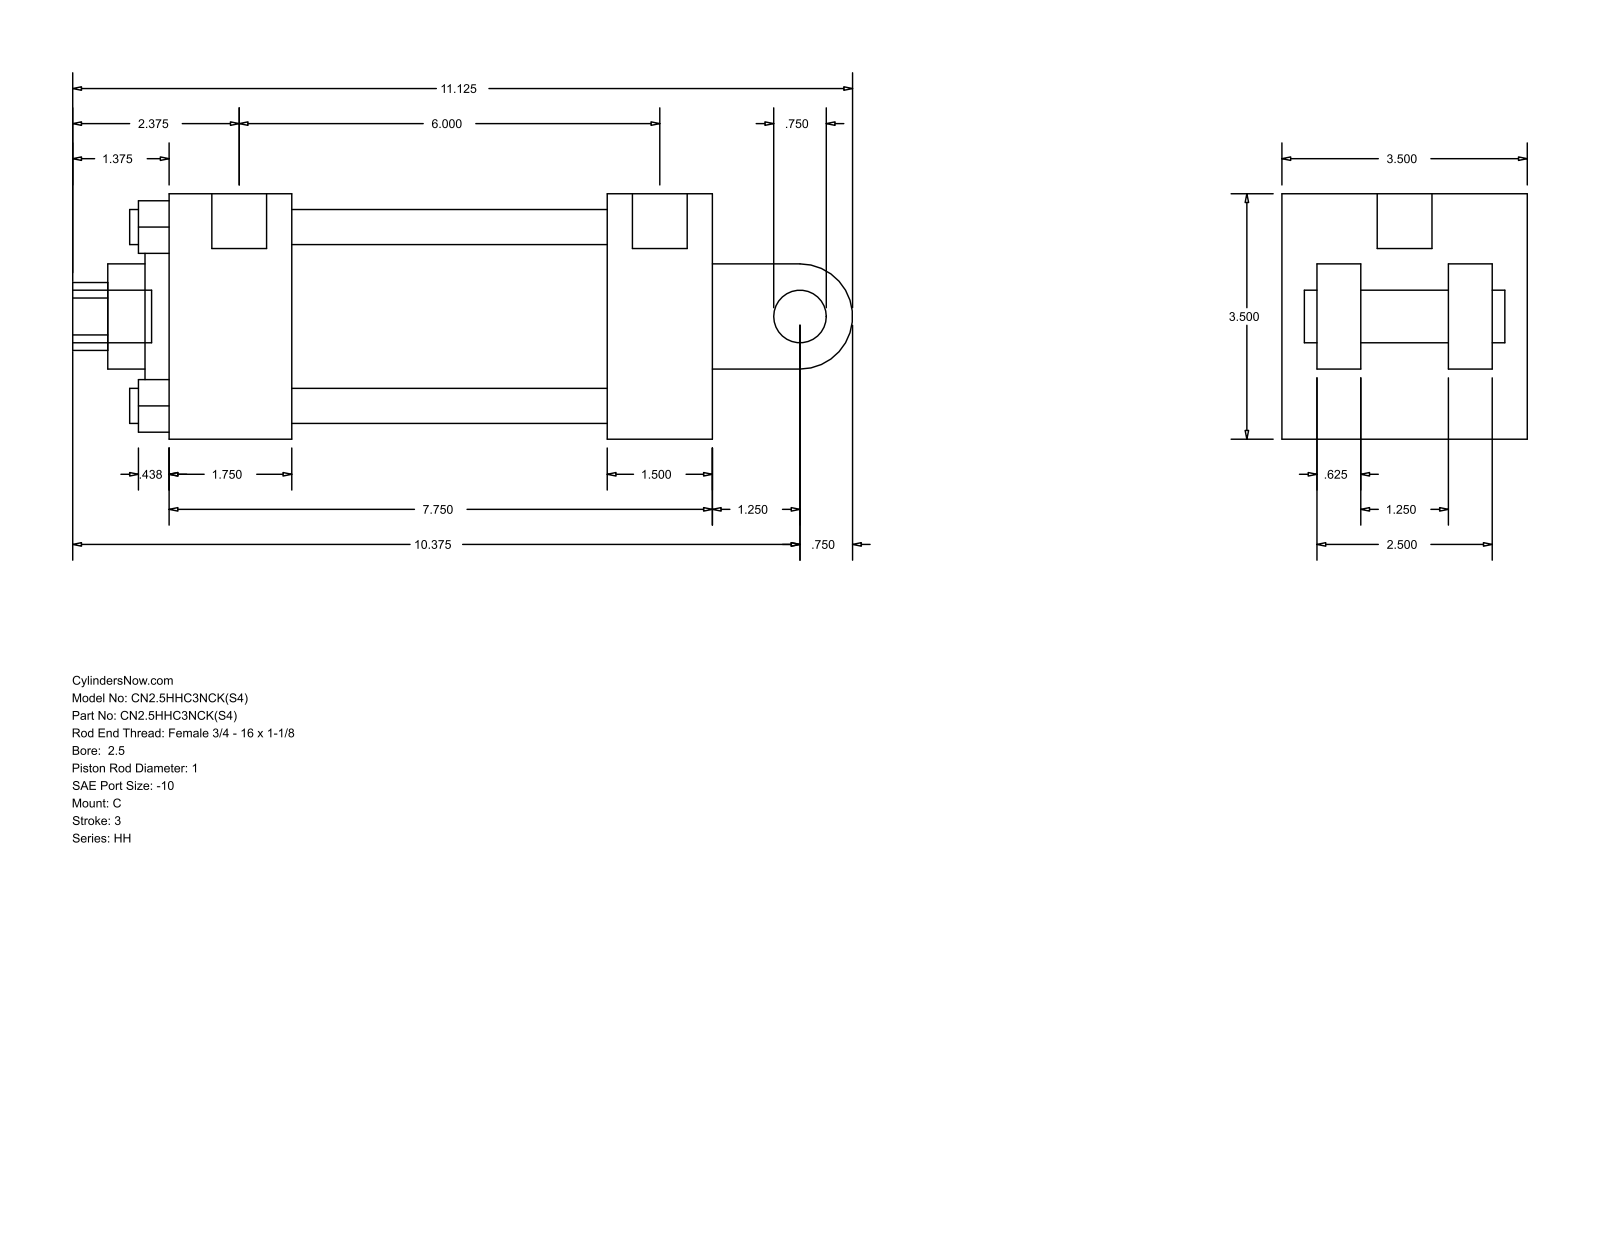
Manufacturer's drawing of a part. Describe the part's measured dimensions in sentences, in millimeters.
The part is named "HH_C__0250_1". Its 3-D file was written by "GSSL Pune (CONFIG_CONTROL_DESIGN)". It is 0 solids with 101 faces: 71 planar, 30 cylindrical and 0 other. Overall it measures 282.57 by 88.9 by 88.9 millimeters. Round holes: 4 of diameter 12.7, 2 of diameter 5.56, 1 of diameter 19.84, 1 of diameter 25.4, 1 of diameter 38.1, 1 of diameter 60.33, 1 of diameter 73.03. Round bosses or shafts: 2 of diameter 19.05, 2 of diameter 5.56, 1 of diameter 19.84. Partial cylindrical surfaces (rounded edges, fillets, slot ends): 1 of radius 12.29, 1 of radius 19.05. The main face-to-face distances are 88.9, 38.1, 196.86, 63.5, 15.87, 158.76, 44.46, 114.3, 152.4, 28.57. The hole center spacings are 45.79, 64.76, 91.58, 1.59.
